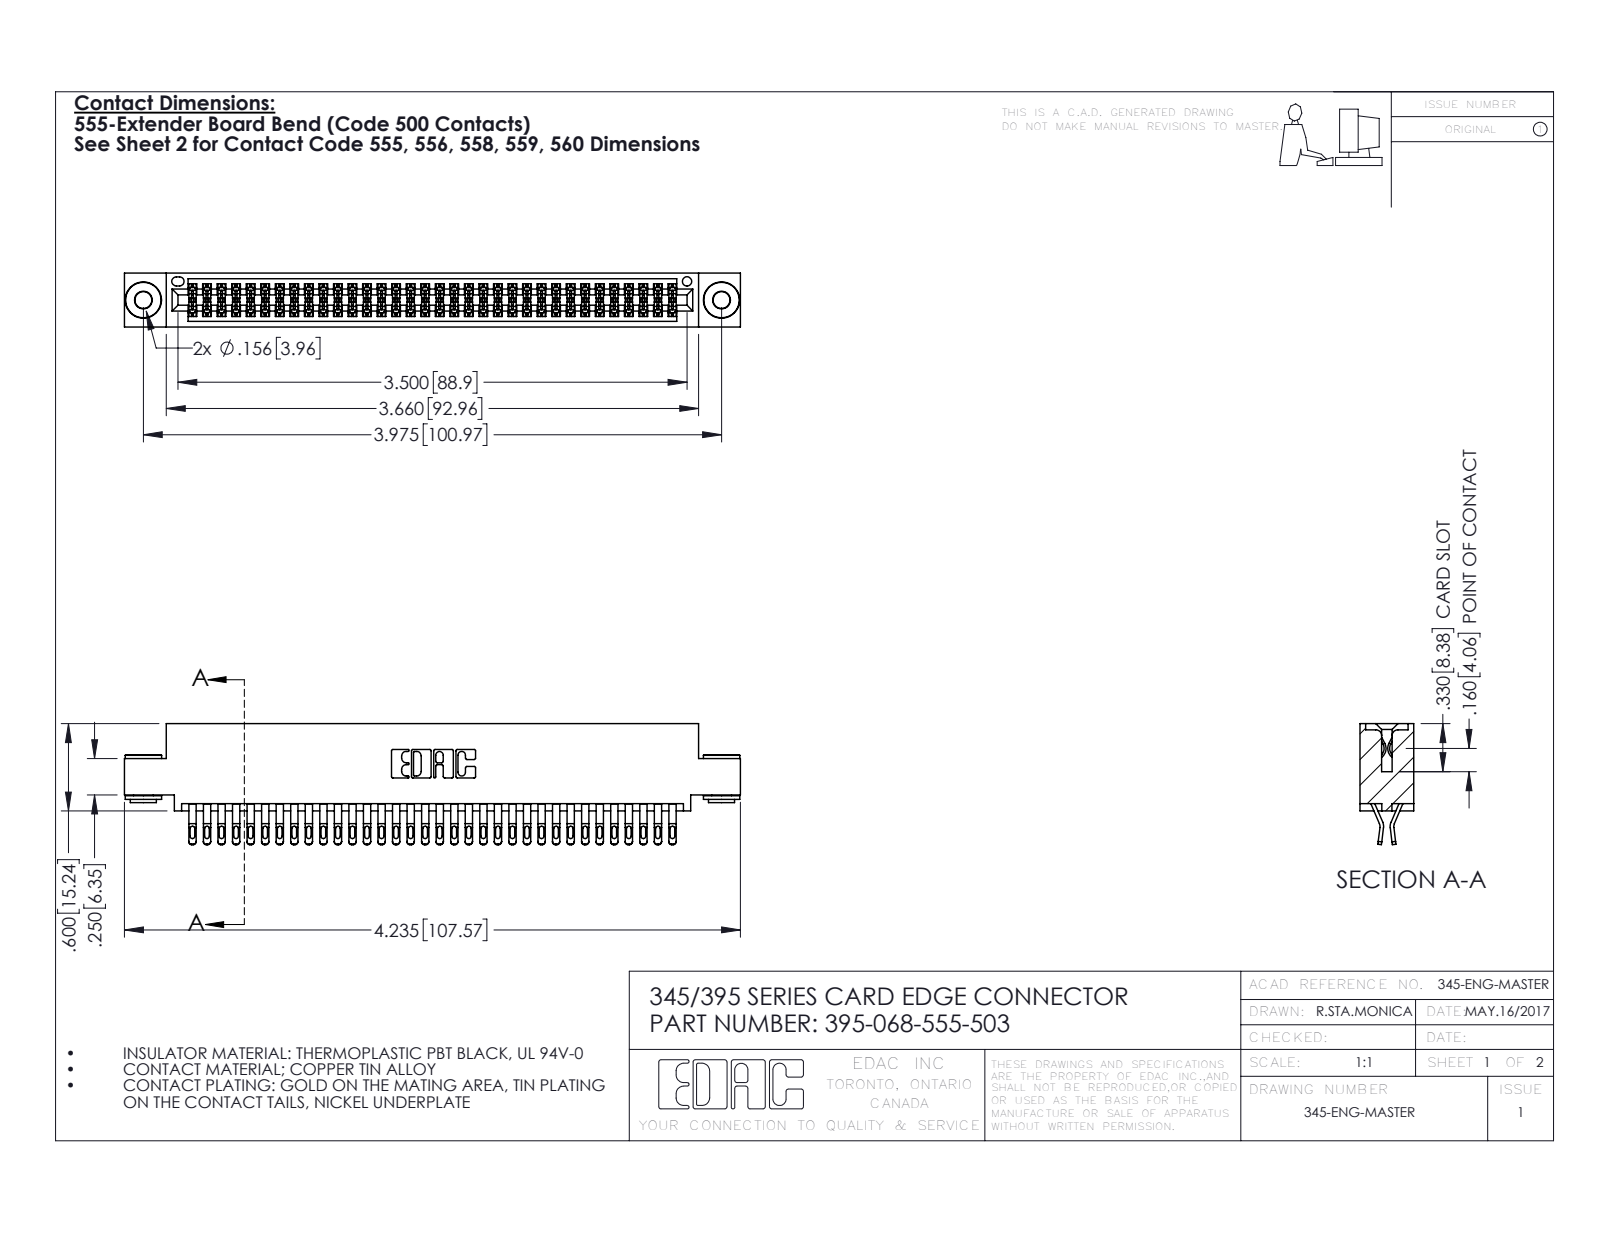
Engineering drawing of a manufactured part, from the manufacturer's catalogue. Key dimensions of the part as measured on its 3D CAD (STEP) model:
Part name (STEP PRODUCT): 345-292-001_555 Tail; 345-250-002_345-250-002-102; 395-068-555-503; 345 Part_0.110 Offset - 0.156 Dia-TH
STEP written by: SolidWorks 2016 (CONFIG_CONTROL_DESIGN)
Units: inches
Bodies: 71 solids, 3976 faces (2202 planar, 1766 cylindrical, 8 other)
Overall size (bounding box): 4.235 × 0.832 × 0.37
Volume: 0.642 in³ · Surface area: 25.38 in²
Round holes (diameter × count): ⌀0.116 ×2, ⌀0.156 ×2, ⌀0.064 ×1
Round bosses / shafts (diameter × count): ⌀0.25 ×2, ⌀0.18 ×2, ⌀0.136 ×2
Partial cylindrical surfaces — rounded edges, fillets, slot ends (radius × count): R0.016 ×170, R0.02 ×136, R0.006 ×102, R0.01 ×22, R0.007 ×6, R0.031 ×6, R0.026 ×3, R0.01 ×2
Main face-to-face distances: 0.072, 0.298, 0.025, 0.37, 0.2, 0.098, 0.272, 0.225, 0.175, 0.149
Hole centre spacings: 0.27, 3.74, 3.975
